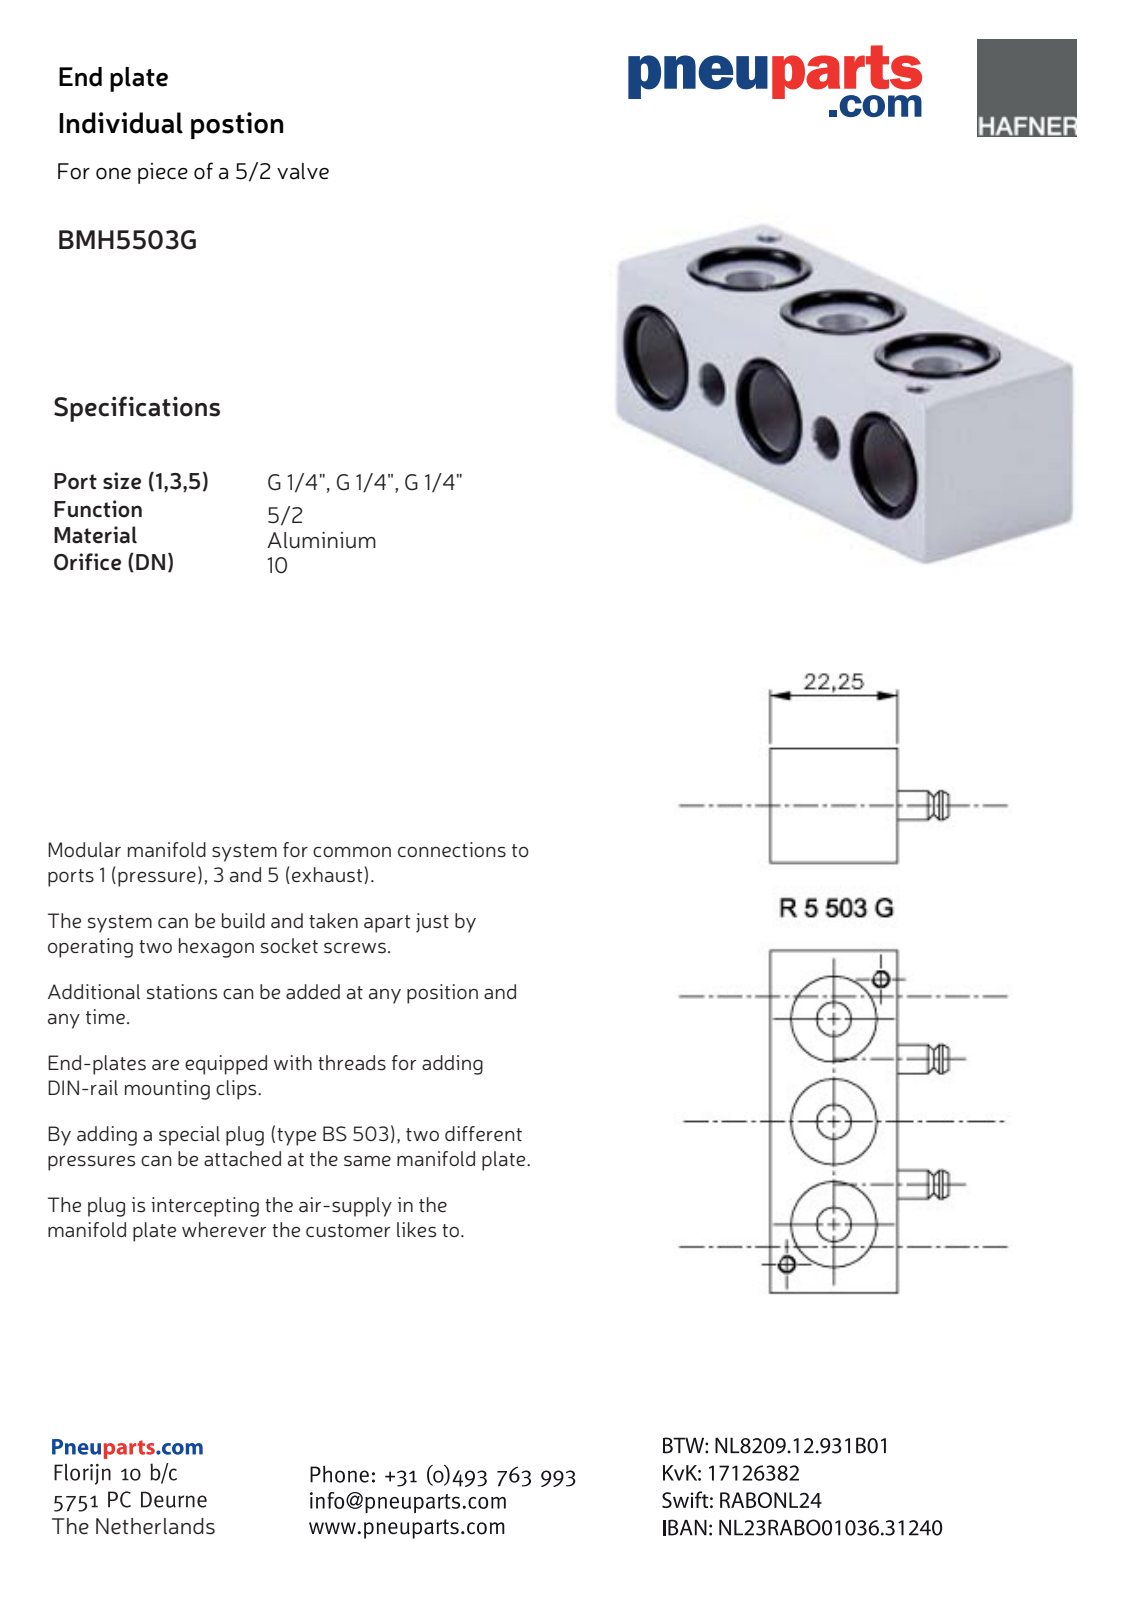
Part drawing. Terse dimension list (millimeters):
written by: Unknown (AUTOMOTIVE_DESIGN)
unit: mm
bodies: 0 solids, 144 faces (76 planar, 30 cylindrical, 38 other)
size: 67.2 × 57.02 × 56.11
holes: 3× ⌀6, 3× ⌀10, 3× ⌀13, 3× ⌀15, 2× ⌀2.46, 2× ⌀4.13
bosses: 4× ⌀5, 2× ⌀5.6, 2× ⌀3, 2× ⌀2.69
face distances: 20, 22.26, 18.8, 1.2, 60, 1.21, 21.05, 2.5, 3.7, 13.55
hole spacings: 22, 8.13, 10.82, 11.75, 18, 26.33, 29.29, 43.78
